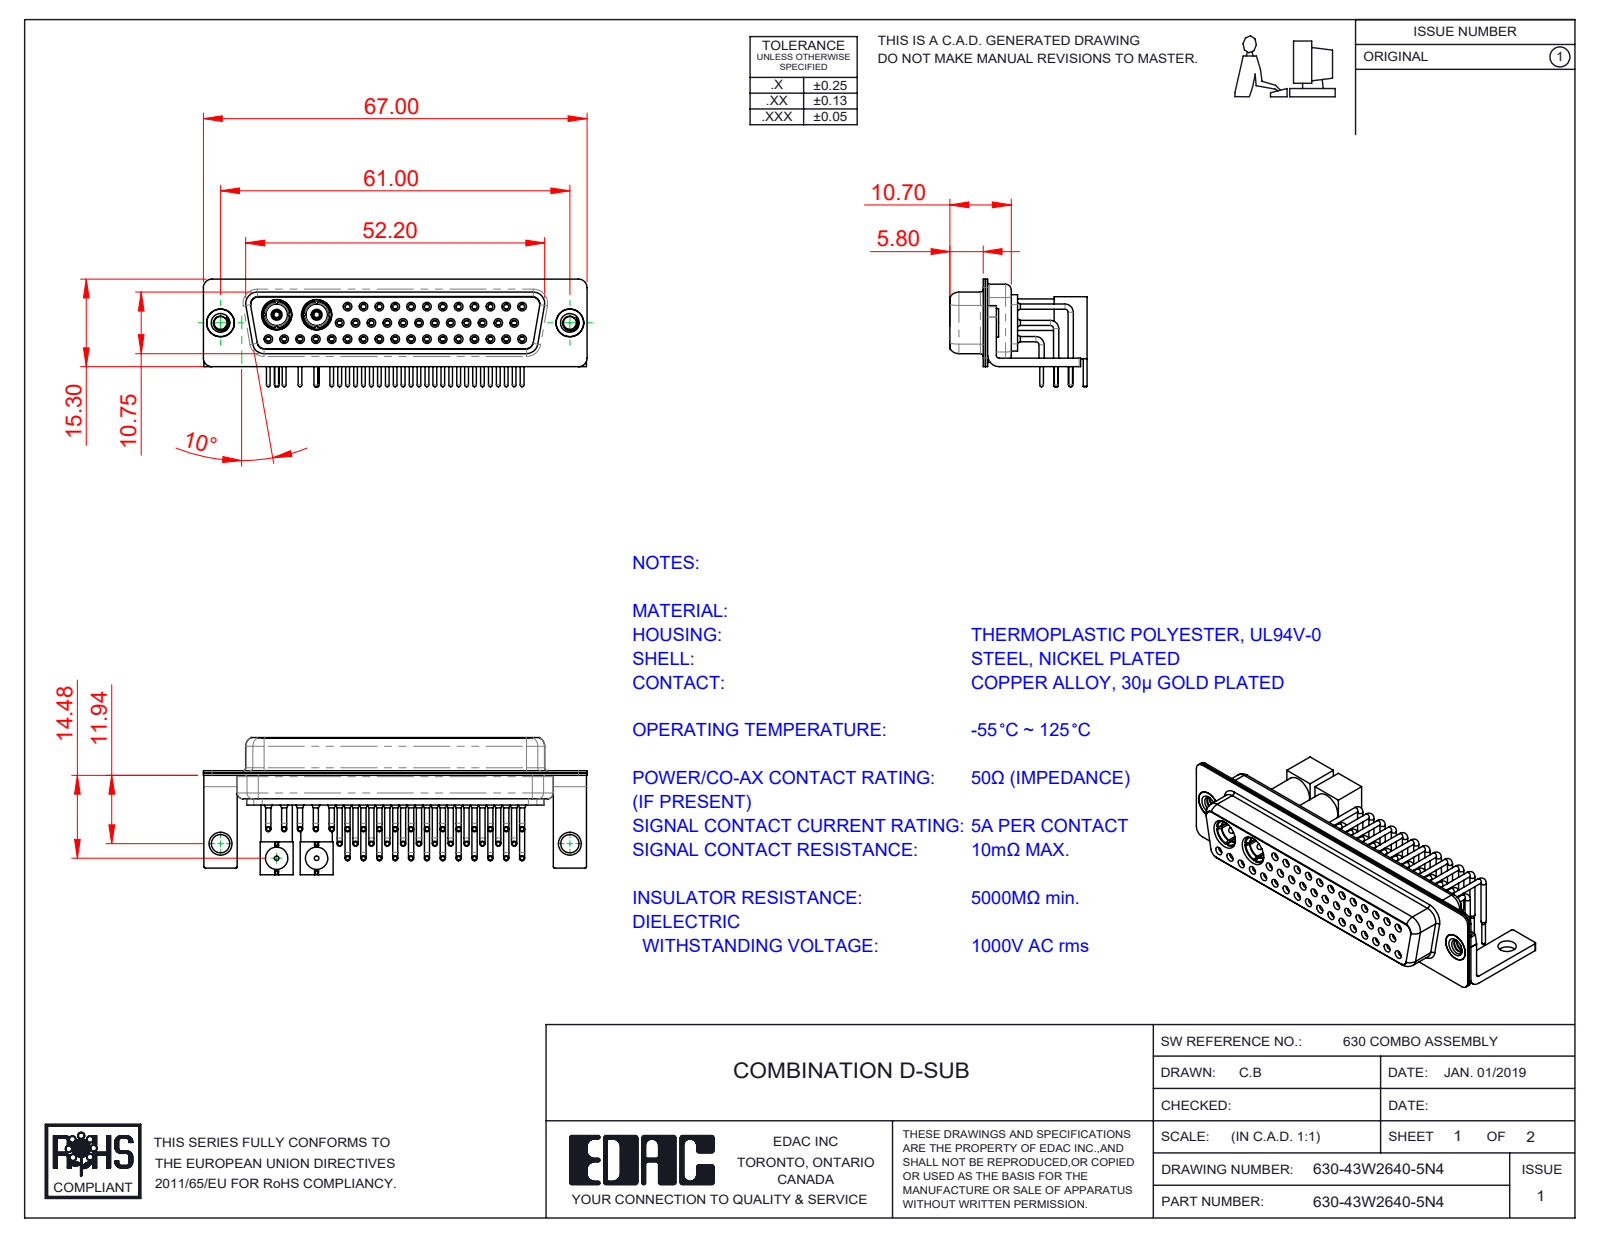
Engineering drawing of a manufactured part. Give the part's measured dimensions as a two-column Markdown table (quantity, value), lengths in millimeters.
| quantity | value |
| --- | --- |
| part name | 630Combo Threaded Rivet_3; 630Combo Housing_43W2; Pin_RA 50; Co-Ax Plug_RA 50 (+8 more) |
| STEP written by | SolidWorks 2020 (CONFIG_CONTROL_DESIGN) |
| units | millimeters |
| bodies | 60 solids, 2828 faces (836 planar, 1228 cylindrical, 764 other) |
| overall size | 67 × 23.95 × 18.8 |
| volume | 8 102 mm³ |
| surface area | 18 103 mm² |
| round holes (diameter × count) | 1.1 × 43, 1.5 × 43, 0.9 × 41, 2 × 41, 1.6 × 29, 1.7 × 12, 4.85 × 4, 0.8 × 2, 2.26 × 2, 2.83 × 2, 3.1 × 2, 3.2 × 2 |
| round bosses / shafts (diameter × count) | 0.9 × 41, 0.65 × 41, 1.6 × 12, 5 × 4, 5.5 × 2, 5.2 × 2, 4.95 × 2, 4.8 × 2 |
| partial cylindrical surfaces (radius × count) | 0.25 × 16, 1.5 × 16, 2 × 13, 1.35 × 12, 1.6 × 8, 0.5 × 5, 0.6 × 4, 0.65 × 4 |
| main face-to-face distances | 0.4, 0.8, 5.6, 6, 1.5, 5.8, 5.2, 11.28, 1.82, 10.35 |
| hole center spacings | 2.77, 3.16, 5.54, 8.31, 11.08, 13.85, 16.62, 19.39 |
